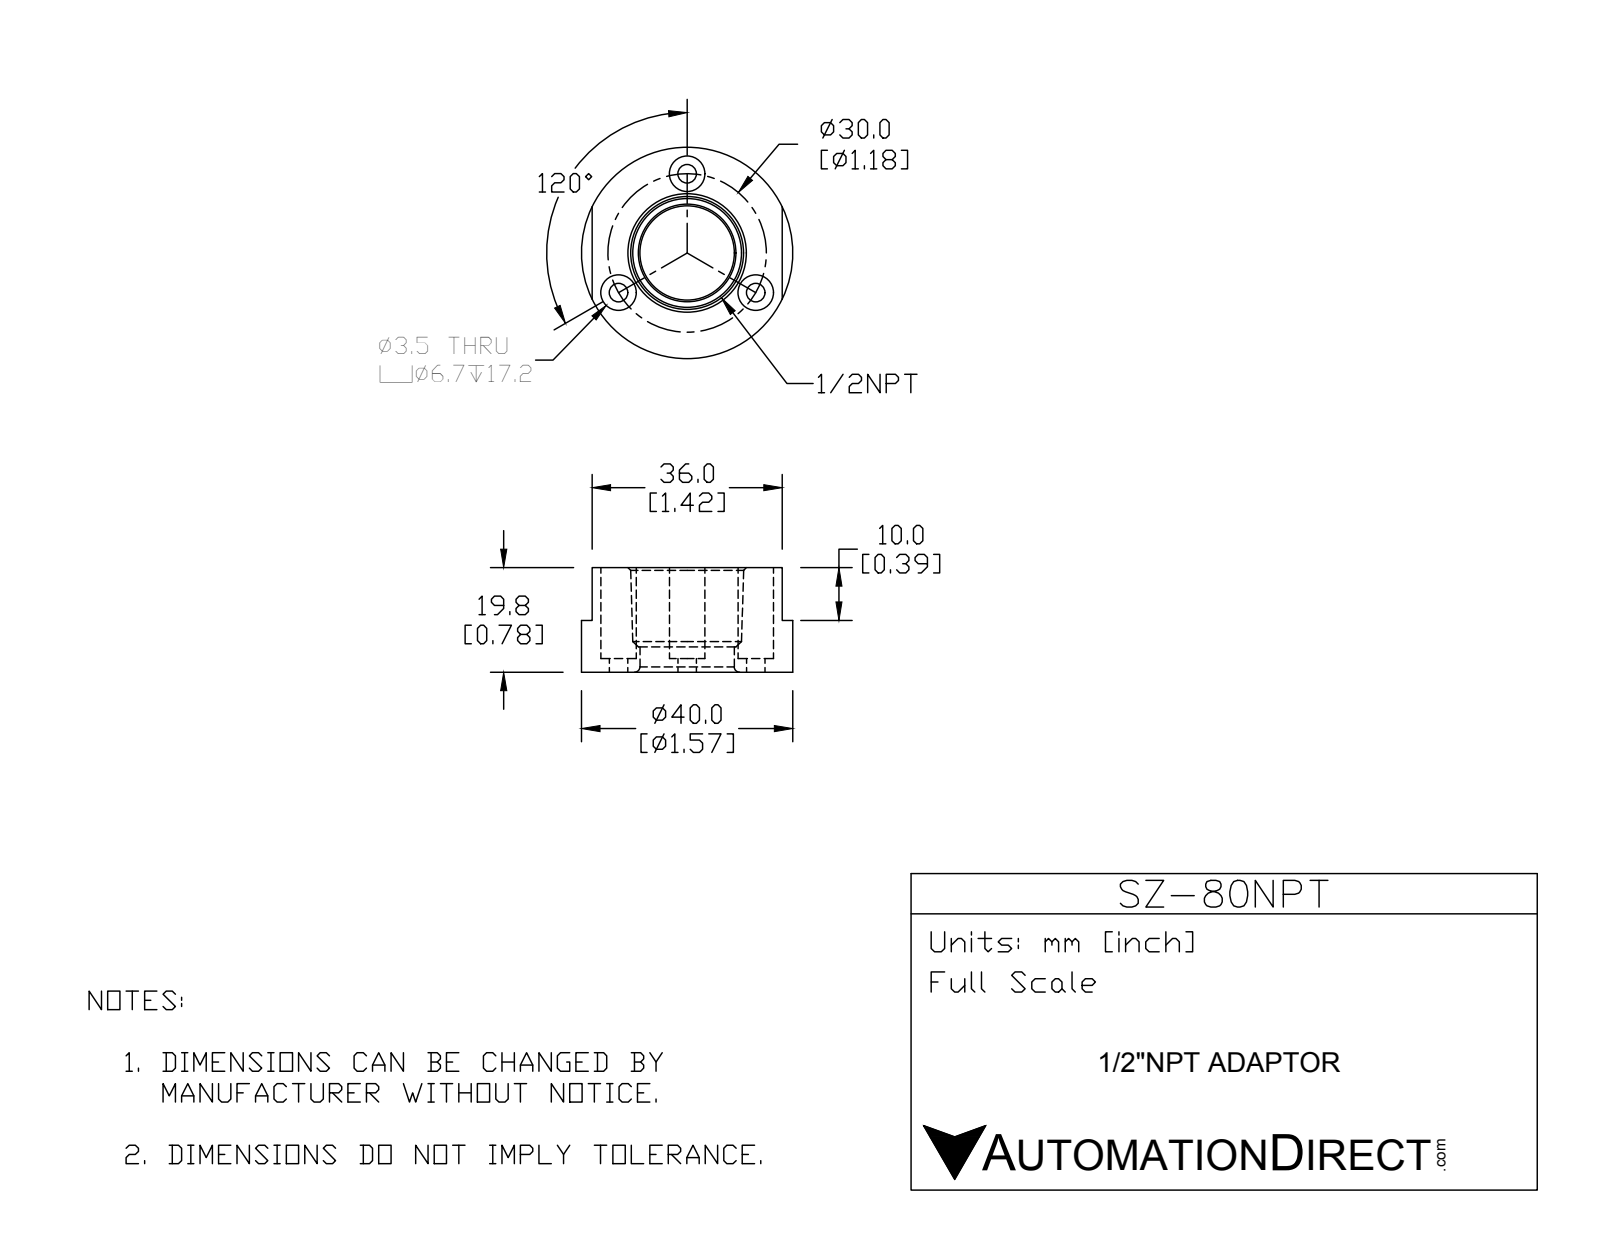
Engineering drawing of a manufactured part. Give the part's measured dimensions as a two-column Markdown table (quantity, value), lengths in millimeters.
| quantity | value |
| --- | --- |
| part name | SZ-80NPT |
| STEP written by | SolidWorks 2016 (AUTOMOTIVE_DESIGN) |
| units | millimeters |
| bodies | 1 solid, 34 faces (10 planar, 16 cylindrical, 8 other) |
| overall size | 40 × 40 × 19.8 |
| volume | 16 138 mm³ |
| surface area | 6 752 mm² |
| round holes (diameter × count) | 3.5 × 3, 6.71 × 3, 17.86 × 1 |
| round bosses / shafts (diameter × count) | 40 × 1 |
| main face-to-face distances | 19.8, 36, 2.6, 17.2, 9.8, 7.2, 10, 4.8, 2.2, 5 |
| hole center spacings | 15, 25.98 |
